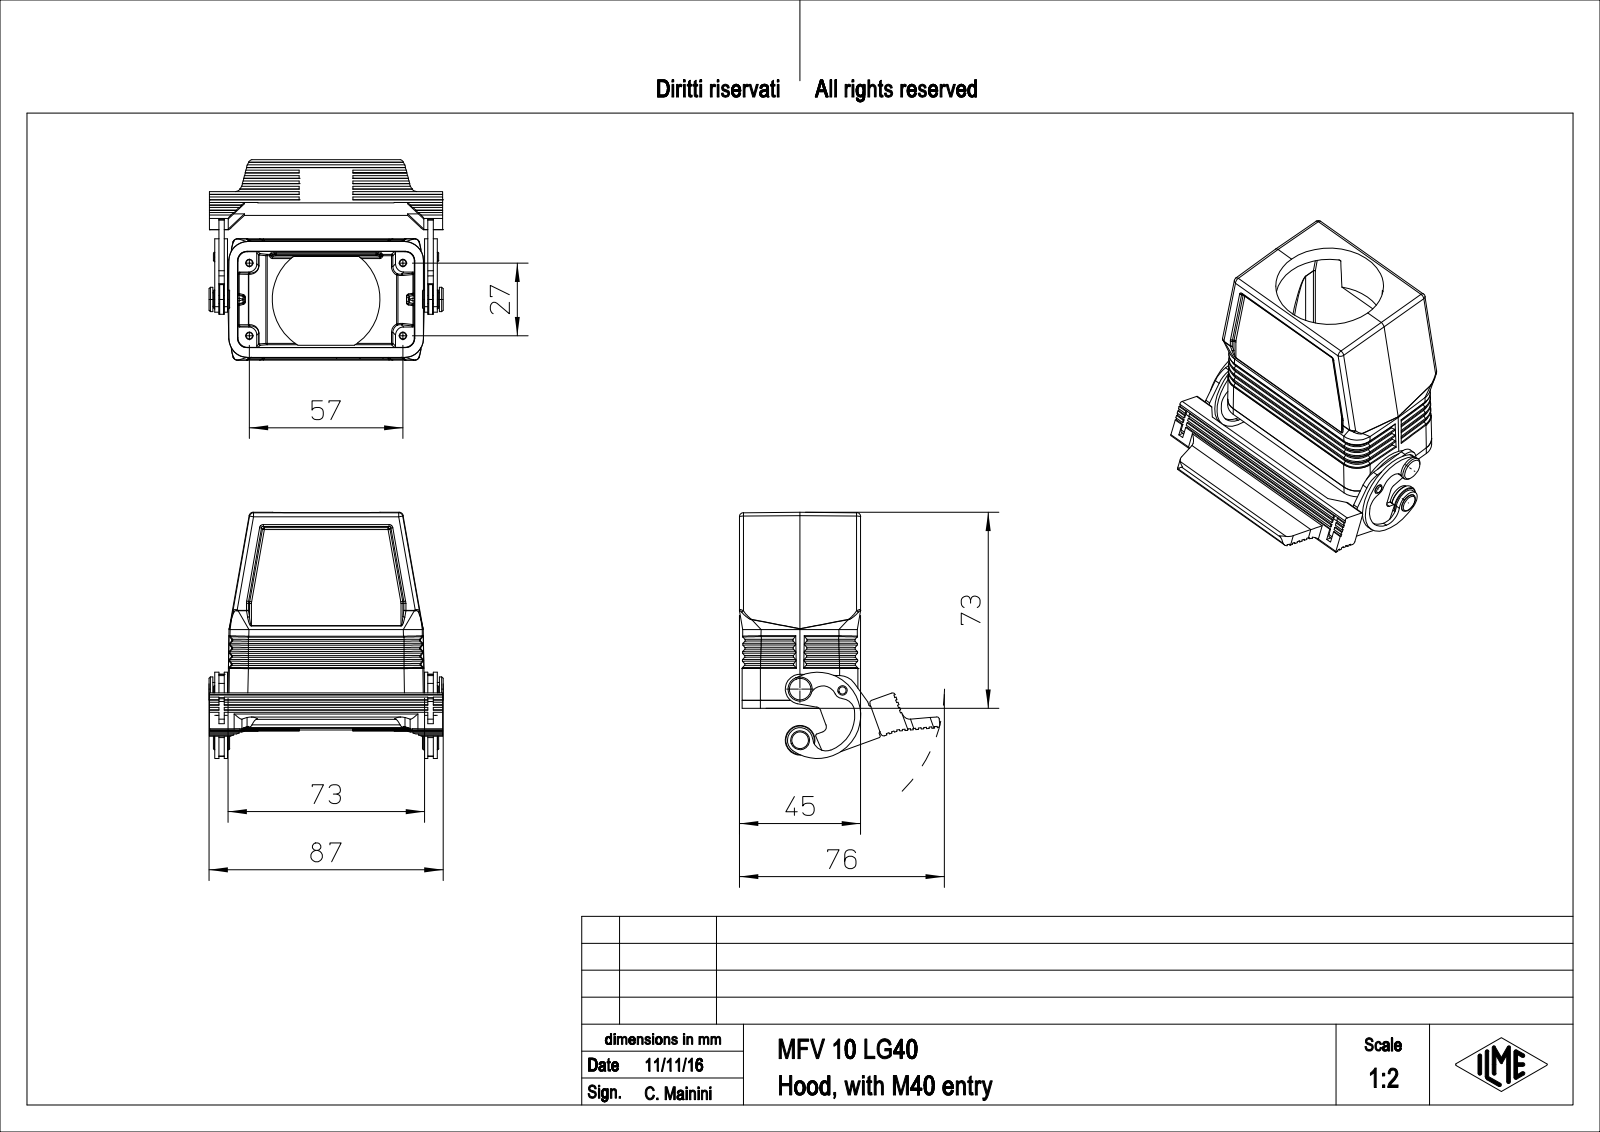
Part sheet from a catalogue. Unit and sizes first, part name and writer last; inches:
Units: inches
Overall size (bounding box): 3.598 × 3.421 × 2.928
Round holes (diameter × count): ⌀0.108 ×4, ⌀0.122 ×1, ⌀0.157 ×1, ⌀0.197 ×1, ⌀1.575 ×1
Round bosses / shafts (diameter × count): ⌀0.433 ×1, ⌀0.354 ×1, ⌀0.276 ×1, ⌀0.197 ×1, ⌀0.138 ×1, ⌀0.118 ×1
Partial cylindrical surfaces — rounded edges, fillets, slot ends (radius × count): R0.02 ×20, R0.059 ×13, R0.276 ×9, R0.118 ×8, R0.039 ×5, R0.138 ×4, R0.138 ×4, R0.165 ×4
Main face-to-face distances: 0.079, 1.693, 0.138, 3.055, 0.039, 0.276, 0.157, 0.041, 0.118, 0.059
Hole centre spacings: 1.242, 1.063, 2.244, 2.483, 0.752, 0.954, 1.341
Volume: 5.088 in³ · Surface area: 70.35 in²
Bodies: 1 solid, 729 faces (371 planar, 196 cylindrical, 162 other)
Part name (STEP PRODUCT): MFV_10_LG40
STEP written by: PTC Creo Elements/Direct Modeling 19.0E 27-Jun-2016 (C) Parametric Technology GmbH (AUTOMOTIVE_DESIGN)
